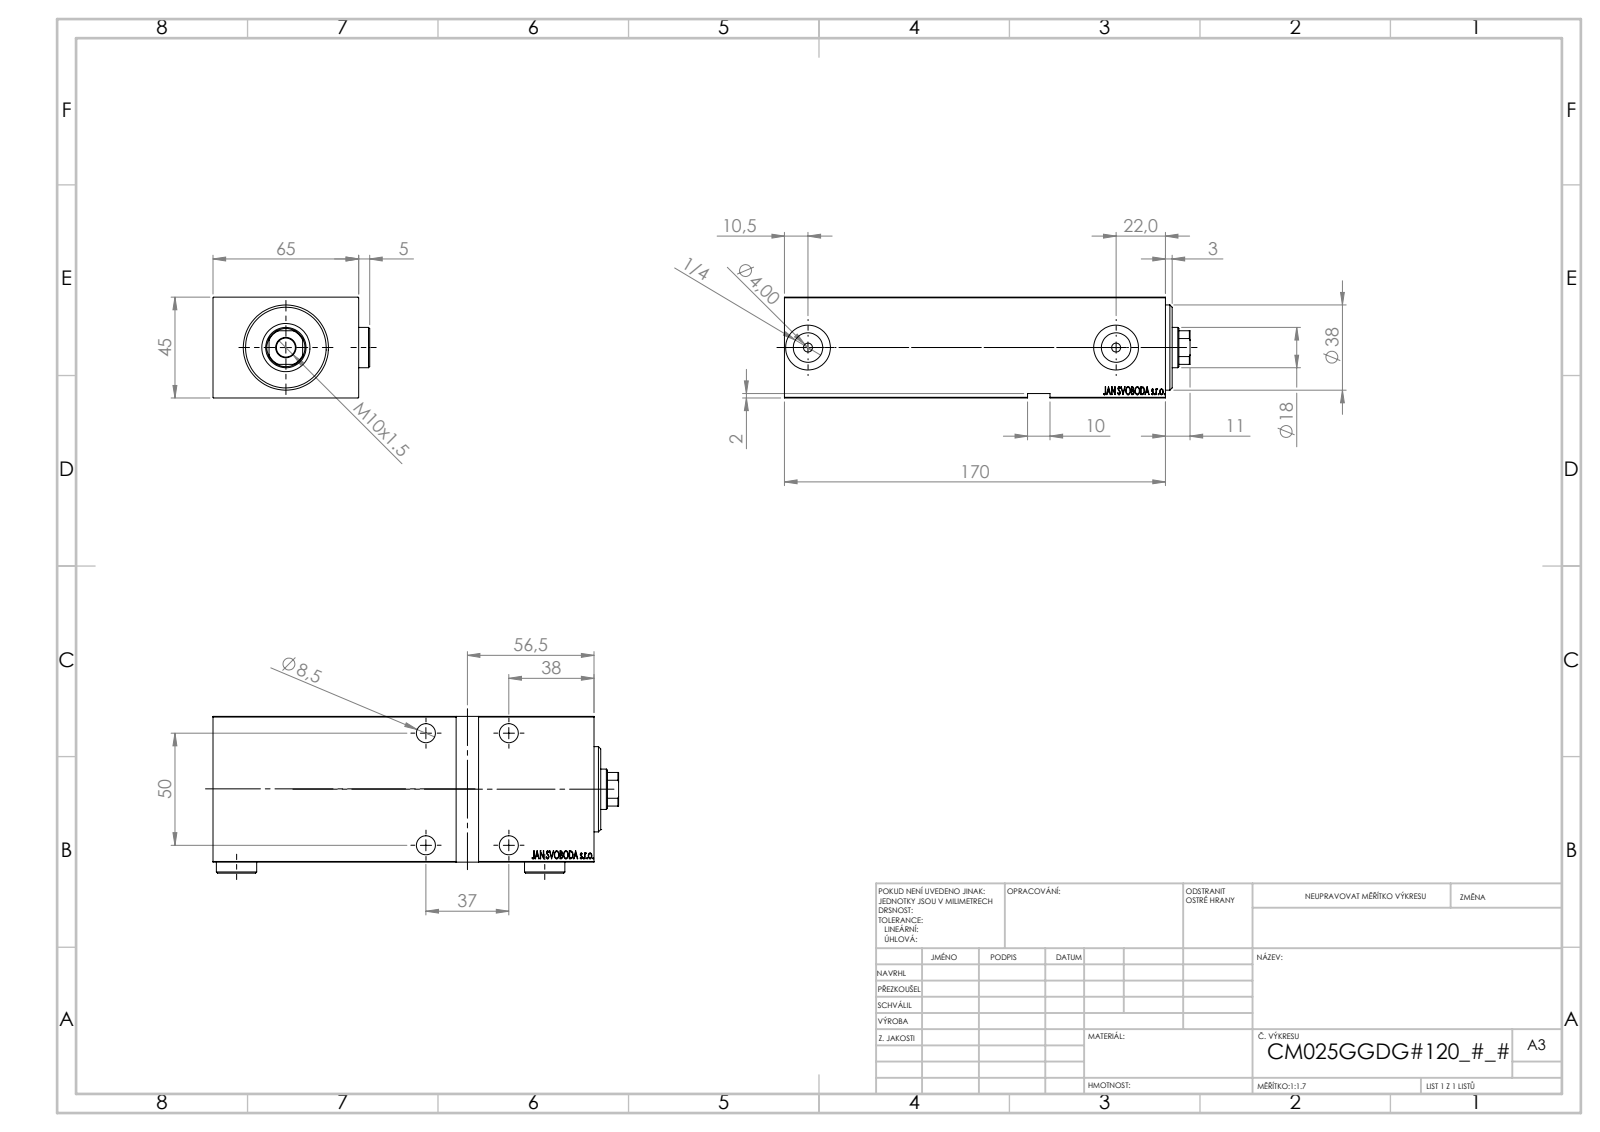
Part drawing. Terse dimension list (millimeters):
name: V450CM_G_VCP; Zatka_OIL_PORT; V450CM_VC_G; V450CM_G_Body
written by: SolidWorks 2019 (CONFIG_CONTROL_DESIGN)
unit: mm
bodies: 5 solids, 913 faces (445 planar, 70 cylindrical, 398 other)
size: 181 × 69.9 × 45
volume: 452 066 mm³; area: 81 576 mm²
holes: 5× ⌀8.5, 4× ⌀13.5, 2× ⌀4, 2× ⌀13.16, 2× ⌀20, 1× ⌀18, 1× ⌀21.5, 1× ⌀25, 1× ⌀27, 1× ⌀35
bosses: 2× ⌀18, 1× ⌀38
rounds: 1× R8.5
face distances: 45, 65, 170, 6, 64.9, 159, 5, 164, 8, 165
hole spacings: 37, 50, 62.2, 137.5
